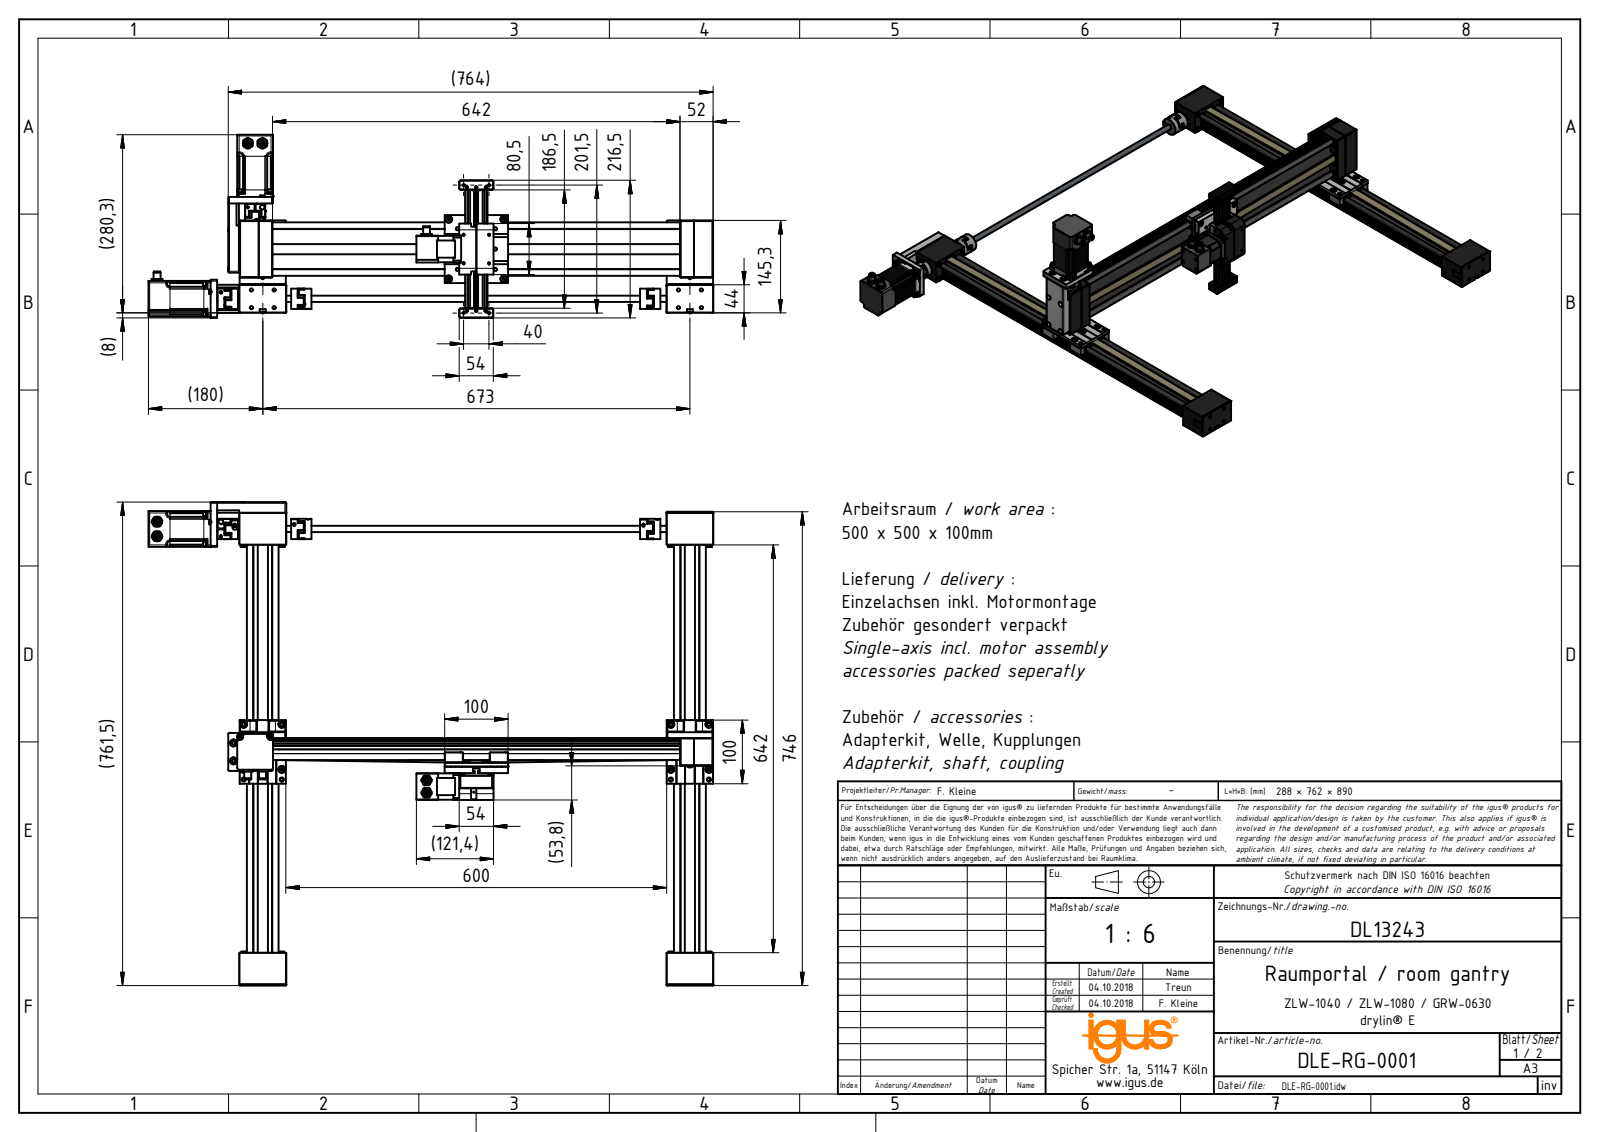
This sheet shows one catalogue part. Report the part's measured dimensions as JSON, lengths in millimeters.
{"part_name": "DLE-RG-0001; ZLW-1040-S-konfig-X1; ZTF-104006; SAXT-104005 (+8 more)", "step_written_by": "Autodesk Inventor 2018 (AUTOMOTIVE_DESIGN)", "units": "millimeters", "bodies": {"solids": 287, "faces": 13091, "planar": 6592, "cylindrical": 4292, "other": 2207}, "overall_size": [890, 761.5, 288.3], "volume_mm3": 3541000, "surface_area_mm2": 2115000, "round_holes": [[4.92, 52], [10, 31], [6.6, 30], [3.24, 28], [9.5, 24], [11, 24], [2, 23], [5.5, 22], [6, 22], [5, 21], [3, 17], [4, 16]], "round_bosses_or_shafts": [[1, 39], [6, 38], [10, 27], [4, 27], [7, 26], [5, 24], [1.8, 24], [8.5, 20]], "partial_cylinders_radius": [[0.5, 398], [1, 232], [2, 223], [0.2, 176], [0.6, 128], [10, 102], [2.5, 76], [0.4, 66]], "face_to_face_distances": [17.5, 2.8, 26.5, 3, 0.5, 23.5, 15.5, 8.5, 673, 2], "hole_center_spacings": [10.24, 47.14, 71, 16, 33.33, 34.82, 39.19, 39.51]}
